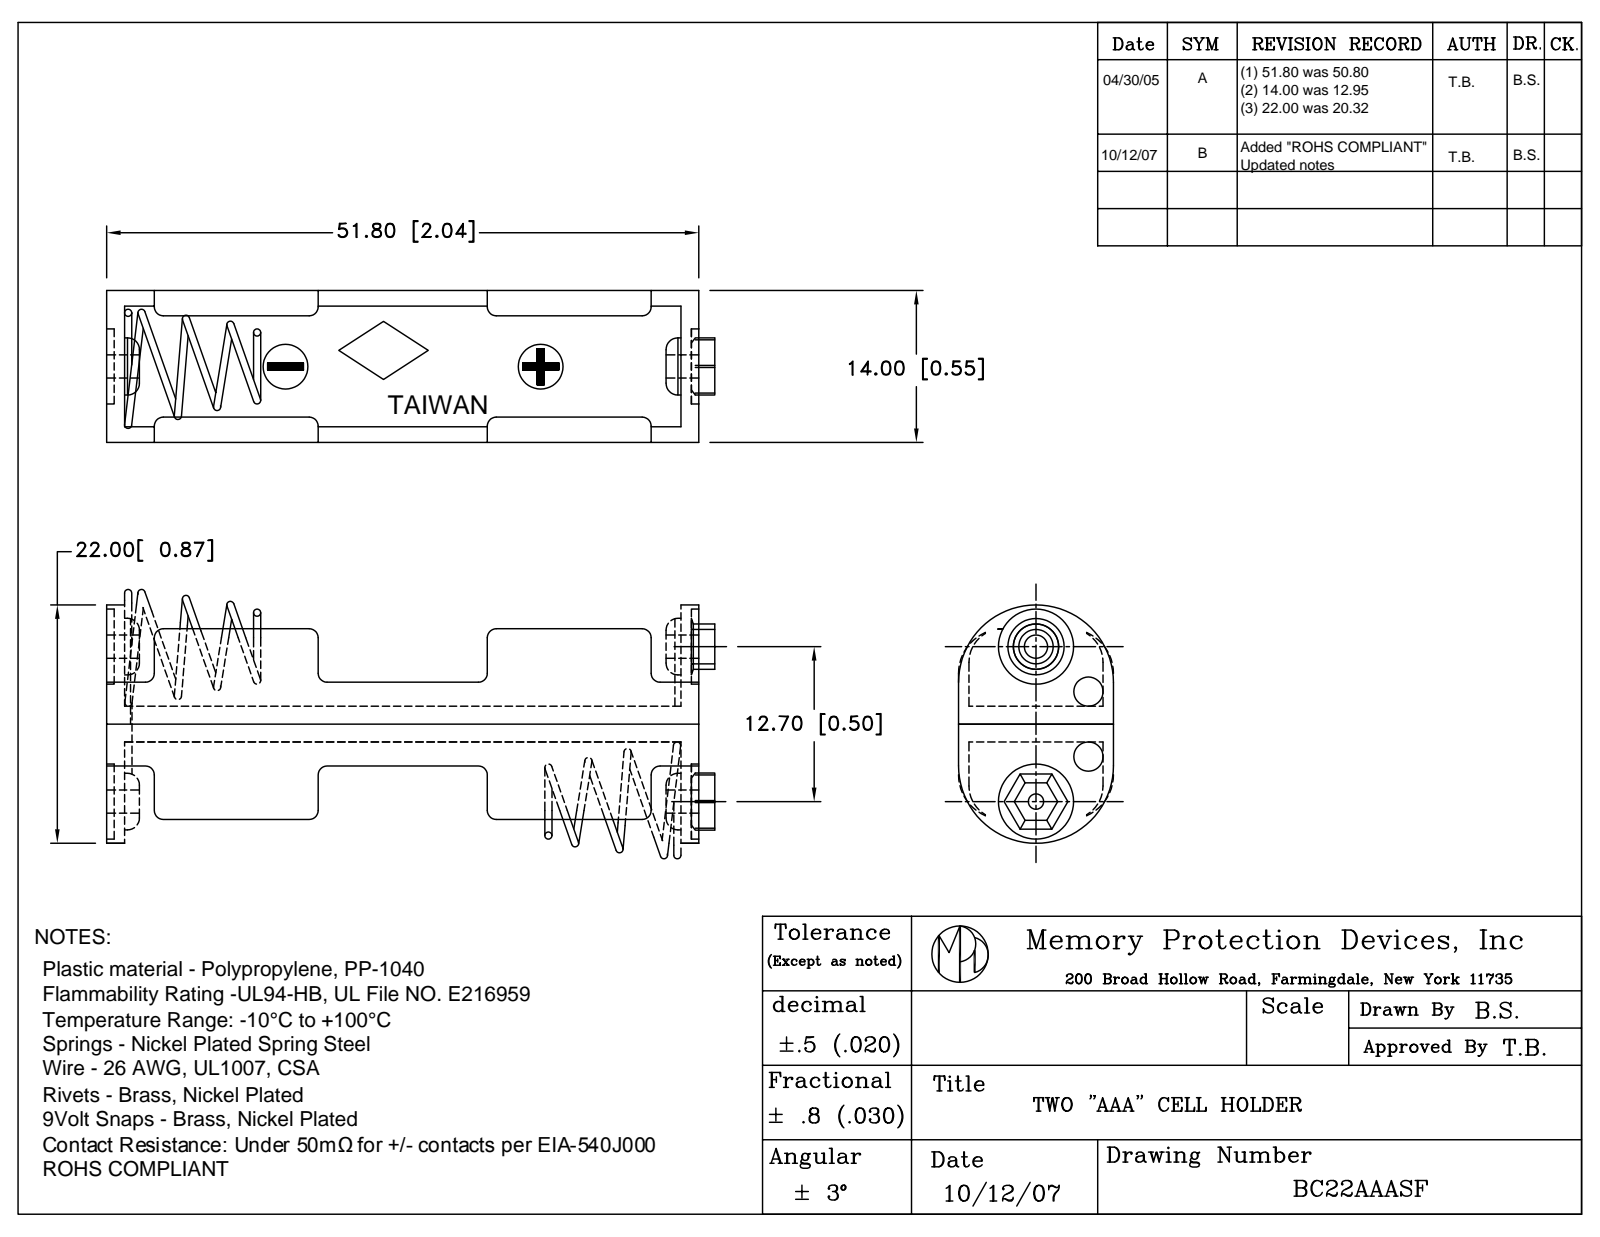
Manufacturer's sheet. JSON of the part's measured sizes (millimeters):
{"part_name": "BC22AAASF", "step_written_by": "SolidWorks 2016 (AUTOMOTIVE_DESIGN)", "units": "millimeters", "bodies": {"solids": 5, "faces": 590, "planar": 223, "cylindrical": 215, "other": 152}, "overall_size": [55.27, 22, 14], "volume_mm3": 3142, "surface_area_mm2": 6566, "round_holes": [[2, 2], [2.3, 2], [2.54, 2], [8.5, 2], [4.95, 1]], "round_bosses_or_shafts": [[6.2, 2], [5, 2], [3.8, 2], [0.63, 2], [7.92, 1], [5.71, 1]], "partial_cylinders_radius": [[1, 24], [0.1, 20], [0.25, 12], [0.38, 12], [0.76, 6], [0.89, 6], [4.31, 4], [6.17, 4]], "face_to_face_distances": [1.3, 12.7, 11.4, 14, 0.99, 50.19, 50.5, 51.49, 0.31, 49.2], "hole_center_spacings": [6.26, 9.38, 3.84, 12.7]}
